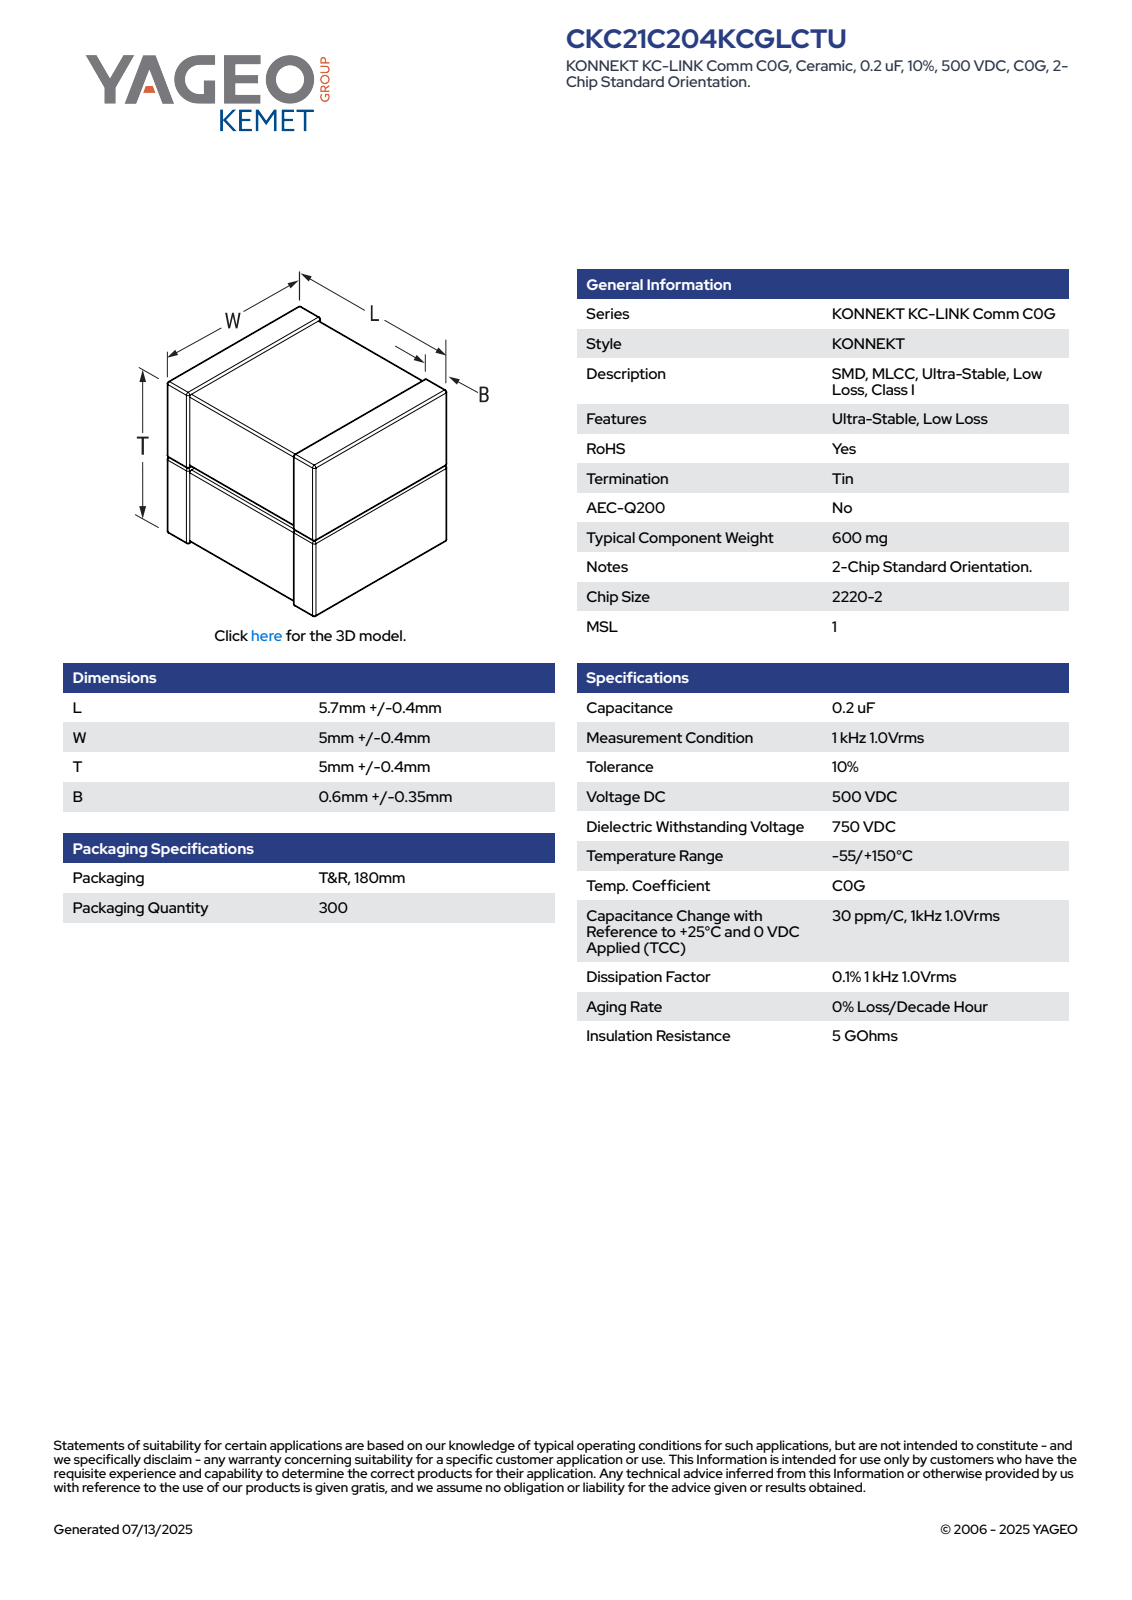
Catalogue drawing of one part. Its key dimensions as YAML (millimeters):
part_name: "CCSS_K2T_2220_L6.1W5.4B0.95T5.4"
step_written_by: "SolidWorks 2020 (AUTOMOTIVE_DESIGN)"
units: millimeters
bodies: {solids: 4, faces: 197, planar: 81, cylindrical: 84, other: 32}
overall_size: [6.1, 5.4, 5.4]
volume: 168
surface_area: 236
face_to_face_distances: [2.56, 2.7, 5.26, 5.33, 6.1, 2.63, 2.77, 5.4, 5.34, 5.27]
